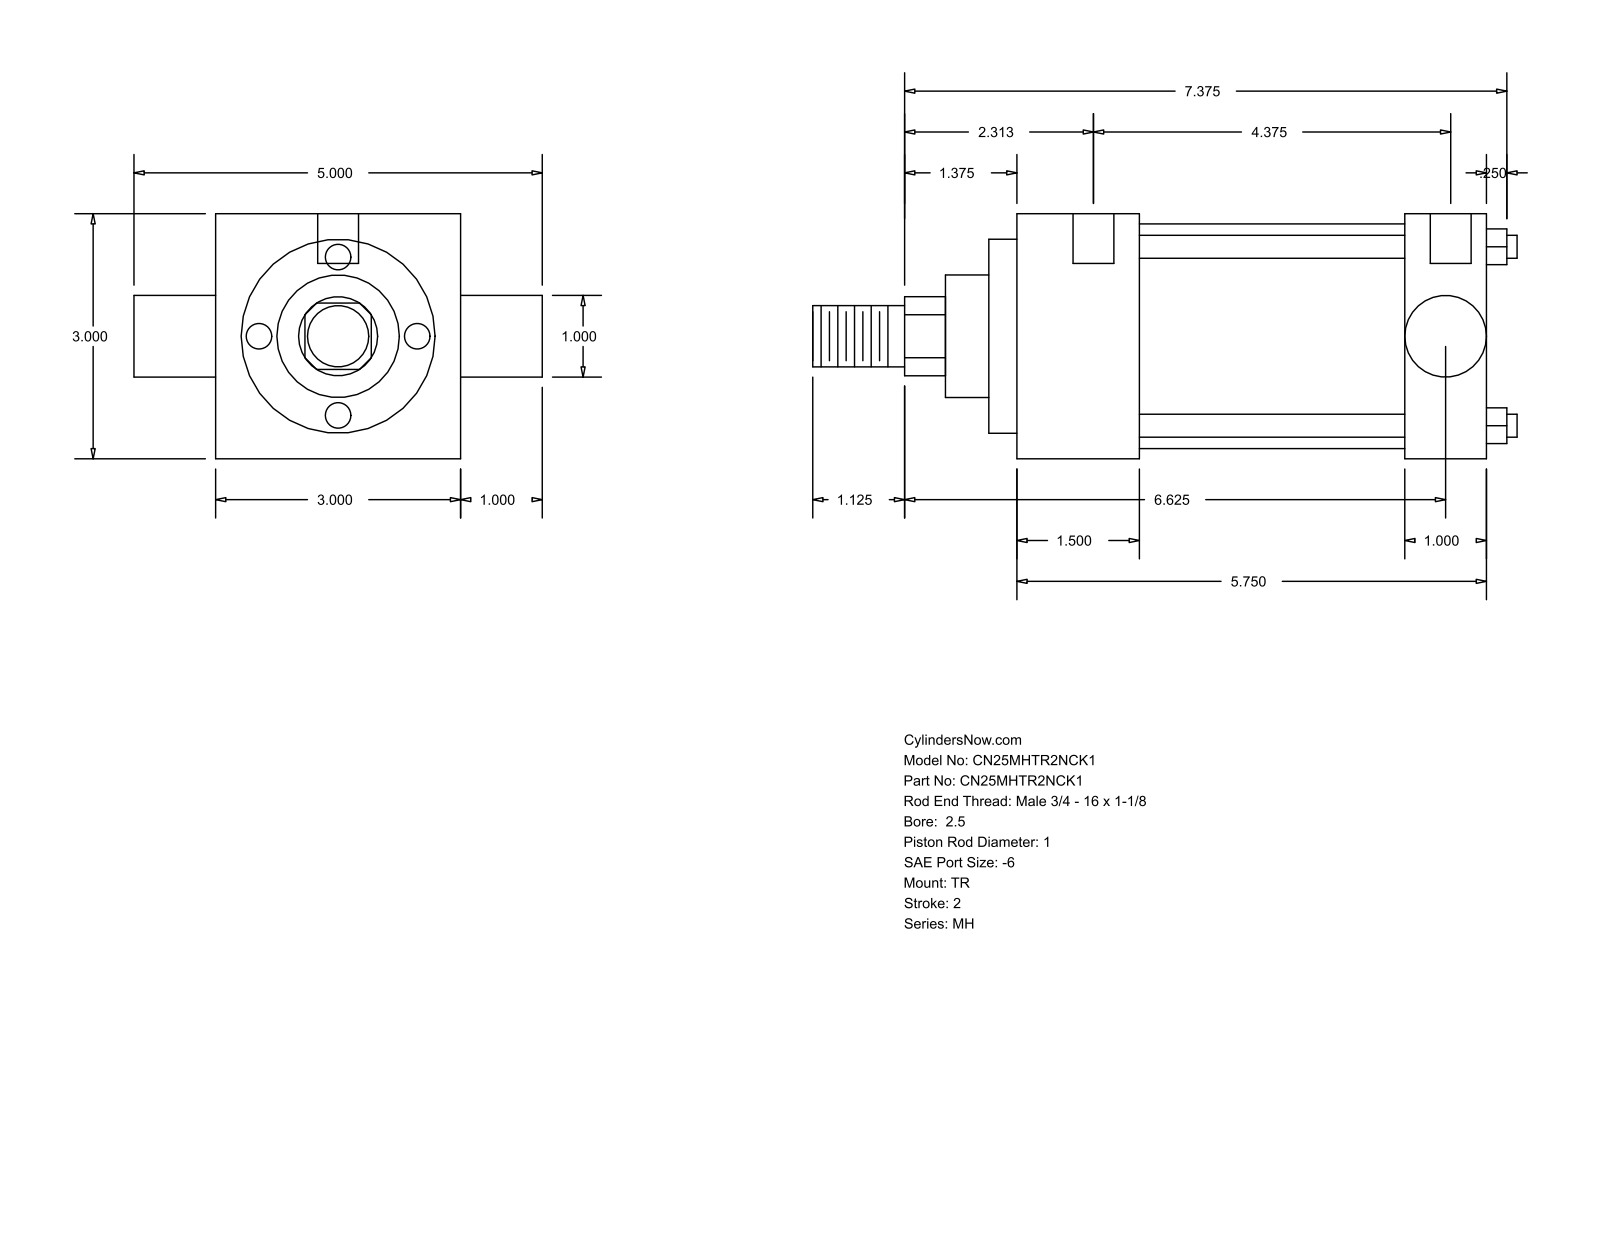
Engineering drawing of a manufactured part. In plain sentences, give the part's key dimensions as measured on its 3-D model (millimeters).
The part is named "MH_TR__0250_1". Its 3-D file was written by "GSSL Pune (CONFIG_CONTROL_DESIGN)". It is 0 solids with 86 faces: 61 planar, 25 cylindrical and 0 other. Overall it measures 219.07 by 127 by 76.2 millimeters. Round holes: 3 of diameter 5.56, 2 of diameter 12.7. Round bosses or shafts: 4 of diameter 7.14, 1 of diameter 69.85, 1 of diameter 60.33, 1 of diameter 38.1, 1 of diameter 25.4, 1 of diameter 25.35, 1 of diameter 19.05. Partial cylindrical surfaces (rounded edges, fillets, slot ends): 1 of radius 12.29. The main face-to-face distances are 76.2, 146.05, 25.4, 38.11, 107.94, 120.65, 82.54, 8.73, 46.84, 129.38. The hole center spacings are 3.18, 4.76, 111.12, 114.3, 115.88, 119.06.
